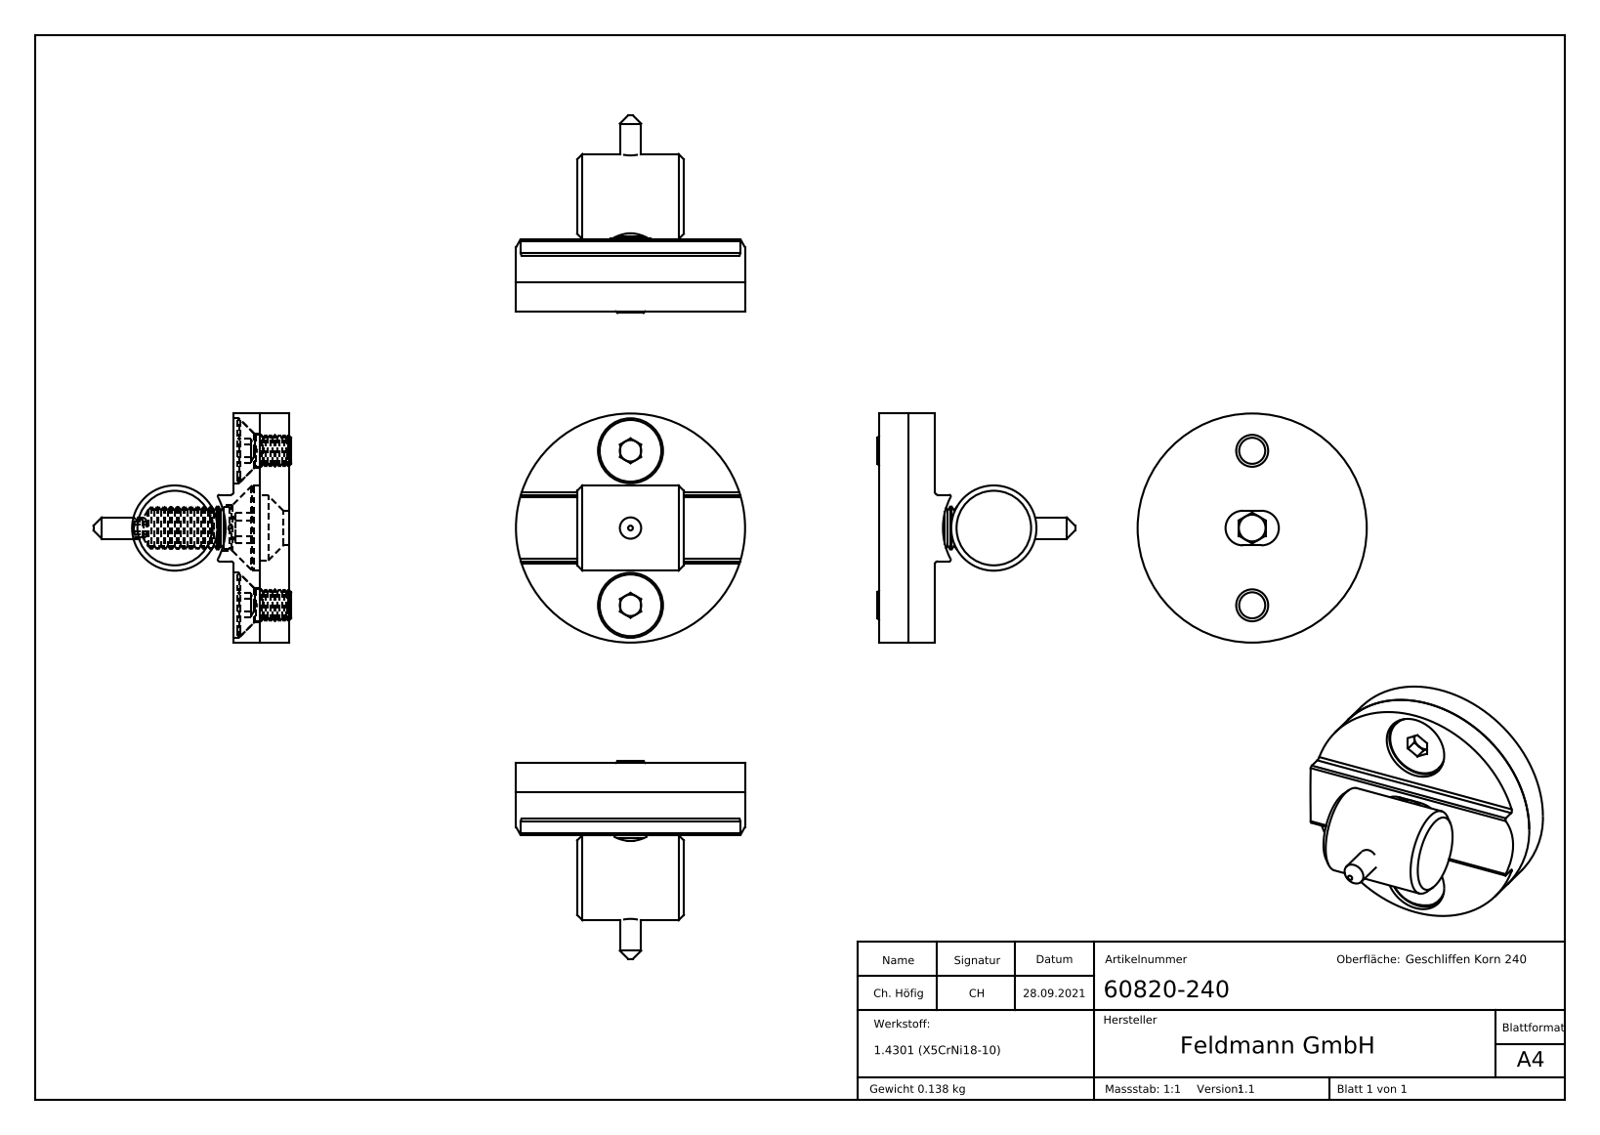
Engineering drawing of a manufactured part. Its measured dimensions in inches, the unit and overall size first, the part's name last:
Units: inches
Overall size (bounding box): 3.744 × 1.693 × 1.693
Round holes (diameter × count): ⌀0.197 ×2, ⌀0.256 ×2, ⌀0.48 ×2, ⌀0.13 ×1, ⌀0.268 ×1
Round bosses / shafts (diameter × count): ⌀0.456 ×2, ⌀0.236 ×2, ⌀1.693 ×1, ⌀0.63 ×1, ⌀0.613 ×1, ⌀0.315 ×1, ⌀0.157 ×1
Partial cylindrical surfaces — rounded edges, fillets, slot ends (radius × count): R0.012 ×2, R0.02 ×2, R0.128 ×2, R0.167 ×2, R0.24 ×2, R0.315 ×2, R0.492 ×1
Main face-to-face distances: 0.217, 0.413, 0.197, 0.787, 0.165, 0.382, 0.031, 0.043, 0.26, 0.154
Hole centre spacings: 0.571, 1.142
Volume: 1.162 in³ · Surface area: 17.82 in²
Bodies: 7 solids, 425 faces (185 planar, 52 cylindrical, 188 other)
Part name (STEP PRODUCT): 60820-240 Teil3; socket countersunk head screw_din; 60820-240 Teil2; 60820-240 (+8 more)
STEP written by: SolidWorks 2018 (CONFIG_CONTROL_DESIGN)
